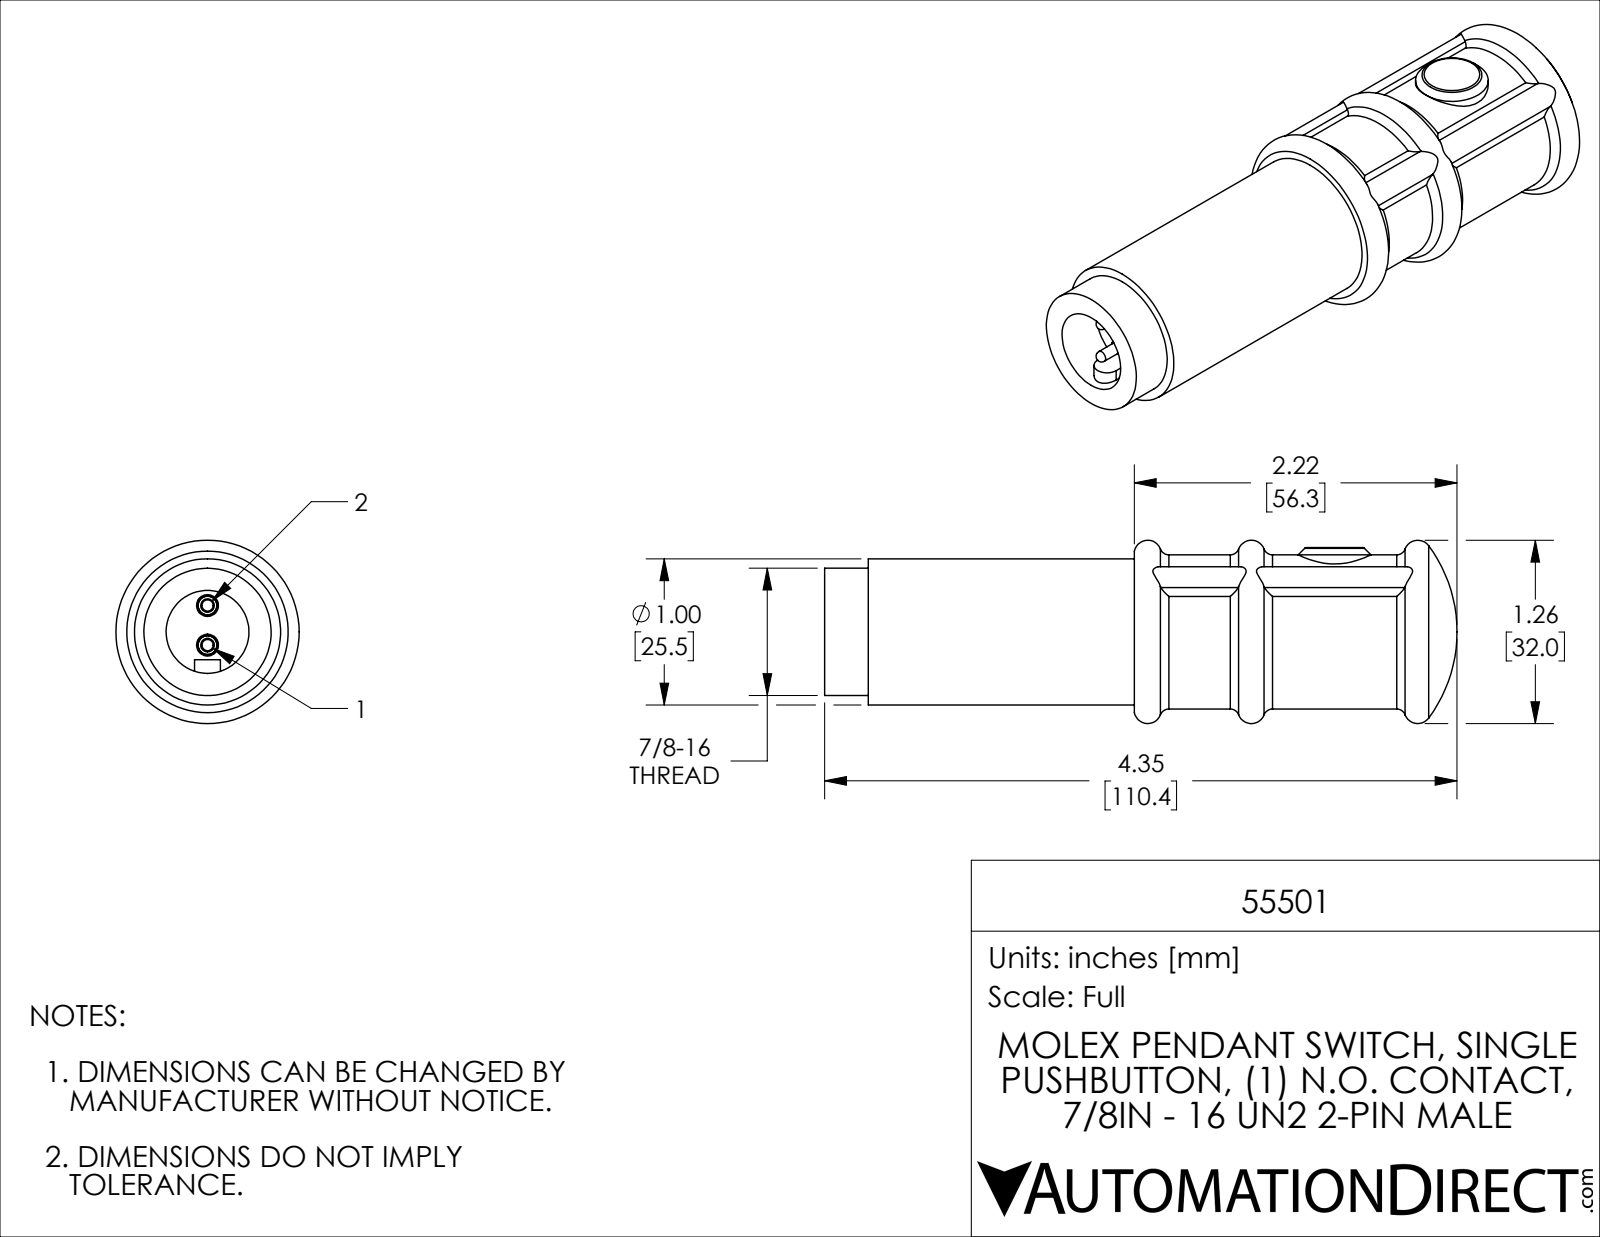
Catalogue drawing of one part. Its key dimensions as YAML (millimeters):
part_name: "55501"
step_written_by: "SolidWorks 2021 (CONFIG_CONTROL_DESIGN)"
units: millimeters
bodies: {solids: 3, faces: 88, planar: 12, cylindrical: 38, other: 38}
overall_size: [110.4, 32, 32]
volume: 59960
surface_area: 11620
round_holes:
  - {diameter: 14.5, count: 1}
round_bosses_or_shafts:
  - {diameter: 2, count: 2}
  - {diameter: 26.9, count: 1}
  - {diameter: 25.5, count: 1}
  - {diameter: 22.2, count: 1}
  - {diameter: 12.7, count: 1}
partial_cylinders:
  - {radius: 1.6, count: 4}
  - {radius: 2.4, count: 3}
  - {radius: 2.3, count: 1}
  - {radius: 13.4, count: 1}
face_to_face_distances: [8.5, 7.6, 0.8, 54.1, 46.5, 45.6, 19.6, 4.5, 6.2, 1.4]
